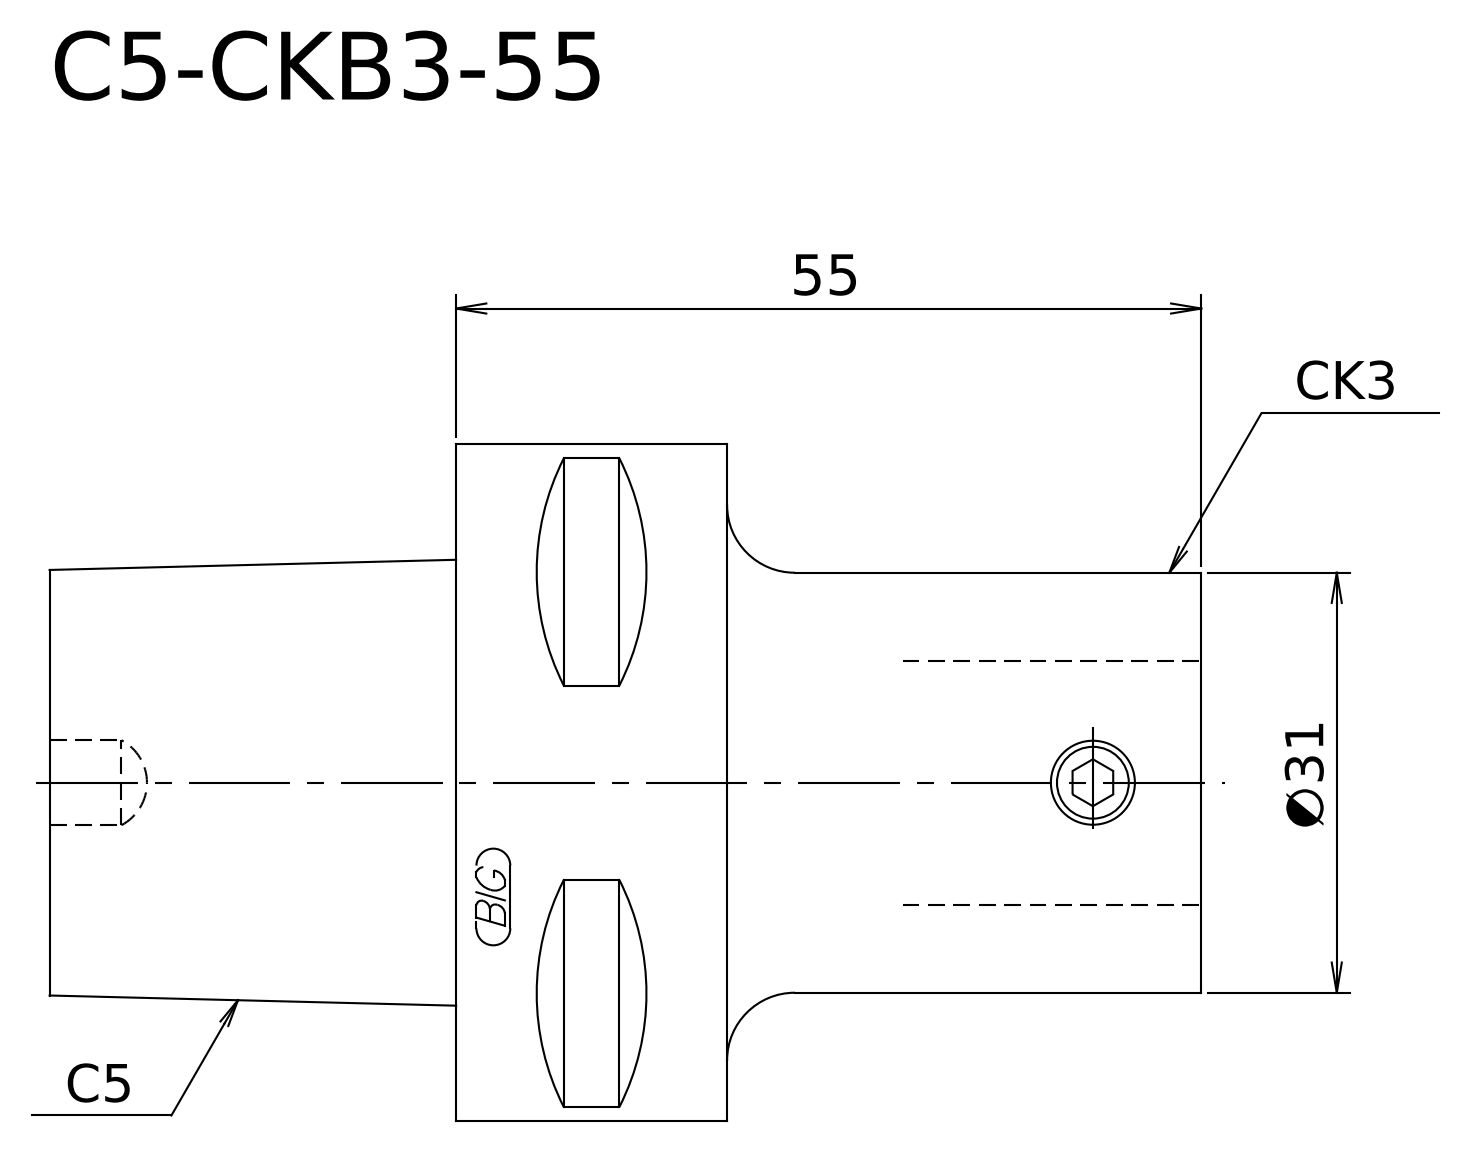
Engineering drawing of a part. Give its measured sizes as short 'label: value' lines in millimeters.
written by: Kubotek KeyCreator V8.5.1 (14335) (CONFIG_CONTROL_DESIGN)
unit: mm
bodies: 1 solid, 8 faces (4 planar, 2 cylindrical, 2 other)
size: 85 × 49.98 × 49.98
volume: 94 213 mm³; area: 13 381 mm²
bosses: 1× ⌀49.98, 1× ⌀31
face distances: 30, 55, 85, 35, 20, 50
